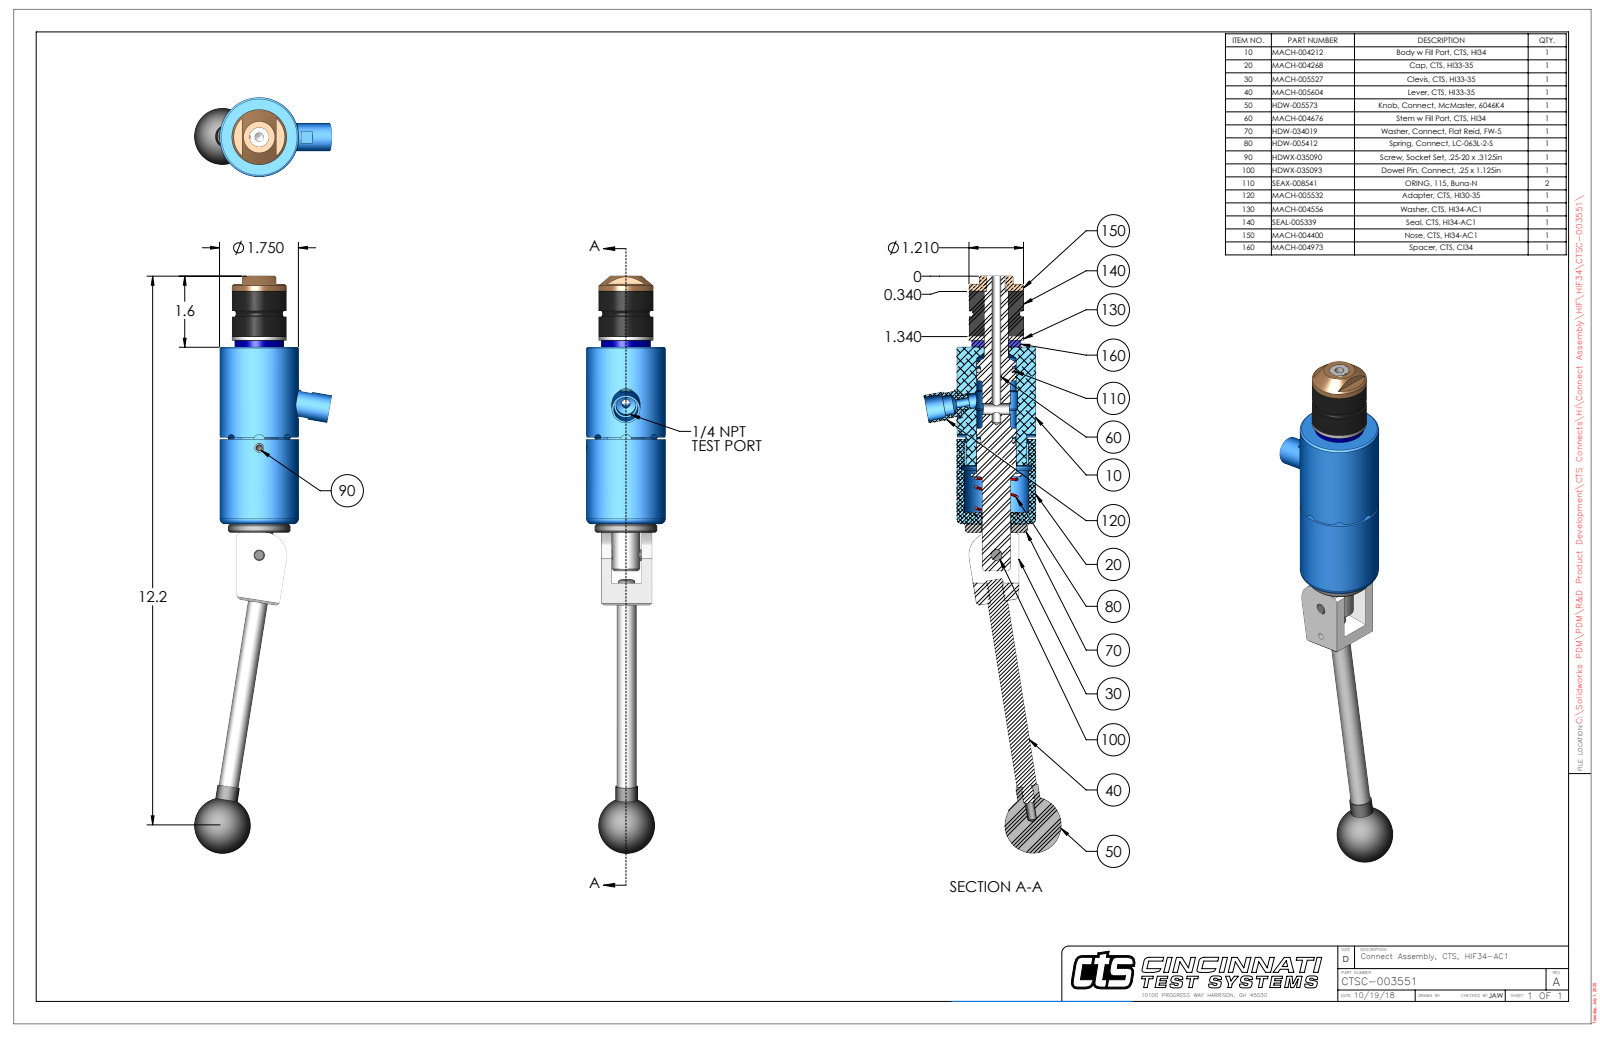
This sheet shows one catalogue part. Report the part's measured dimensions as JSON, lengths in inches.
{"part_name": "CTSC-003551", "step_written_by": "SolidWorks 2023 (AUTOMOTIVE_DESIGN)", "units": "inches", "bodies": {"solids": 10, "faces": 292, "planar": 106, "cylindrical": 121, "other": 65}, "overall_size": [12.795, 3.043, 1.75], "volume_in3": 14.21, "surface_area_in2": 81.06, "round_holes": [[0.201, 2], [0.15, 1], [0.187, 1], [0.204, 1], [0.249, 1], [0.25, 1], [0.251, 1], [0.313, 1], [0.422, 1], [0.438, 1], [0.53, 1], [0.541, 1]], "round_bosses_or_shafts": [[0.5, 2], [0.44, 2], [0.25, 2], [1.75, 1], [1.38, 1], [1.21, 1], [1.09, 1], [0.625, 1]], "partial_cylinders_radius": [[0.125, 4], [0.029, 2], [0.182, 1], [0.33, 1], [0.5, 1], [0.695, 1], [0.823, 1]], "face_to_face_distances": [3.921, 1.237, 5.158, 1, 0.237, 4.158, 1.094, 0.094, 0.143, 4.064], "hole_center_spacings": [0.74, 2.376, 3.116]}
